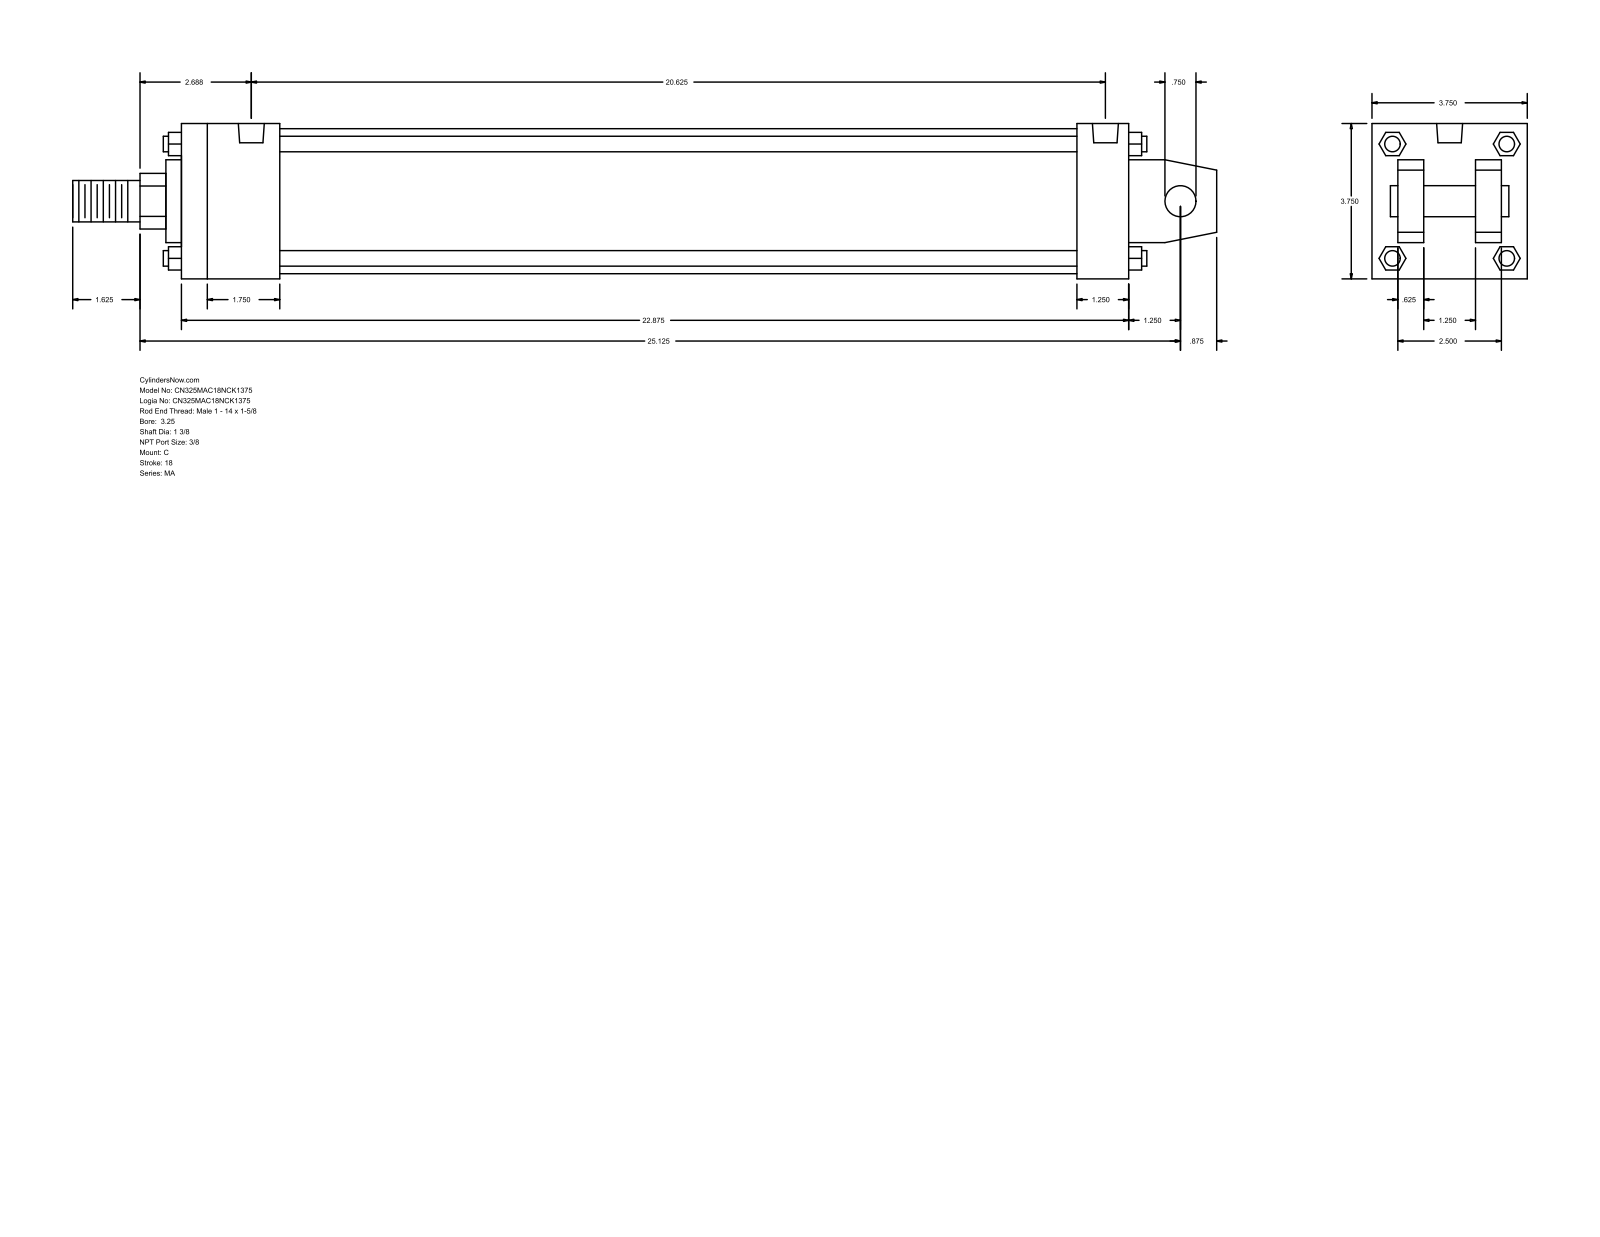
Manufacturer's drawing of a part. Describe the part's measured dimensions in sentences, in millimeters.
The part is named "MA_C__0325_1.375". Its 3-D file was written by "GSSL Pune (CONFIG_CONTROL_DESIGN)". It is 0 solids with 139 faces: 108 planar, 31 cylindrical and 0 other. Overall it measures 701.67 by 95.25 by 95.25 millimeters. Round holes: 4 of diameter 11.11, 2 of diameter 15.93. Round bosses or shafts: 4 of diameter 9.53, 1 of diameter 88.9, 1 of diameter 50.8, 1 of diameter 34.92, 1 of diameter 25.4, 1 of diameter 19.05. Partial cylindrical surfaces (rounded edges, fillets, slot ends): 1 of radius 17.06. The main face-to-face distances are 95.24, 15.87, 63.5, 581.02, 31.74, 79.37, 47.63, 549.27, 31.75, 60.32. The hole center spacings are 514.35, 4.76, 4.77, 519.11, 519.12, 523.88.
